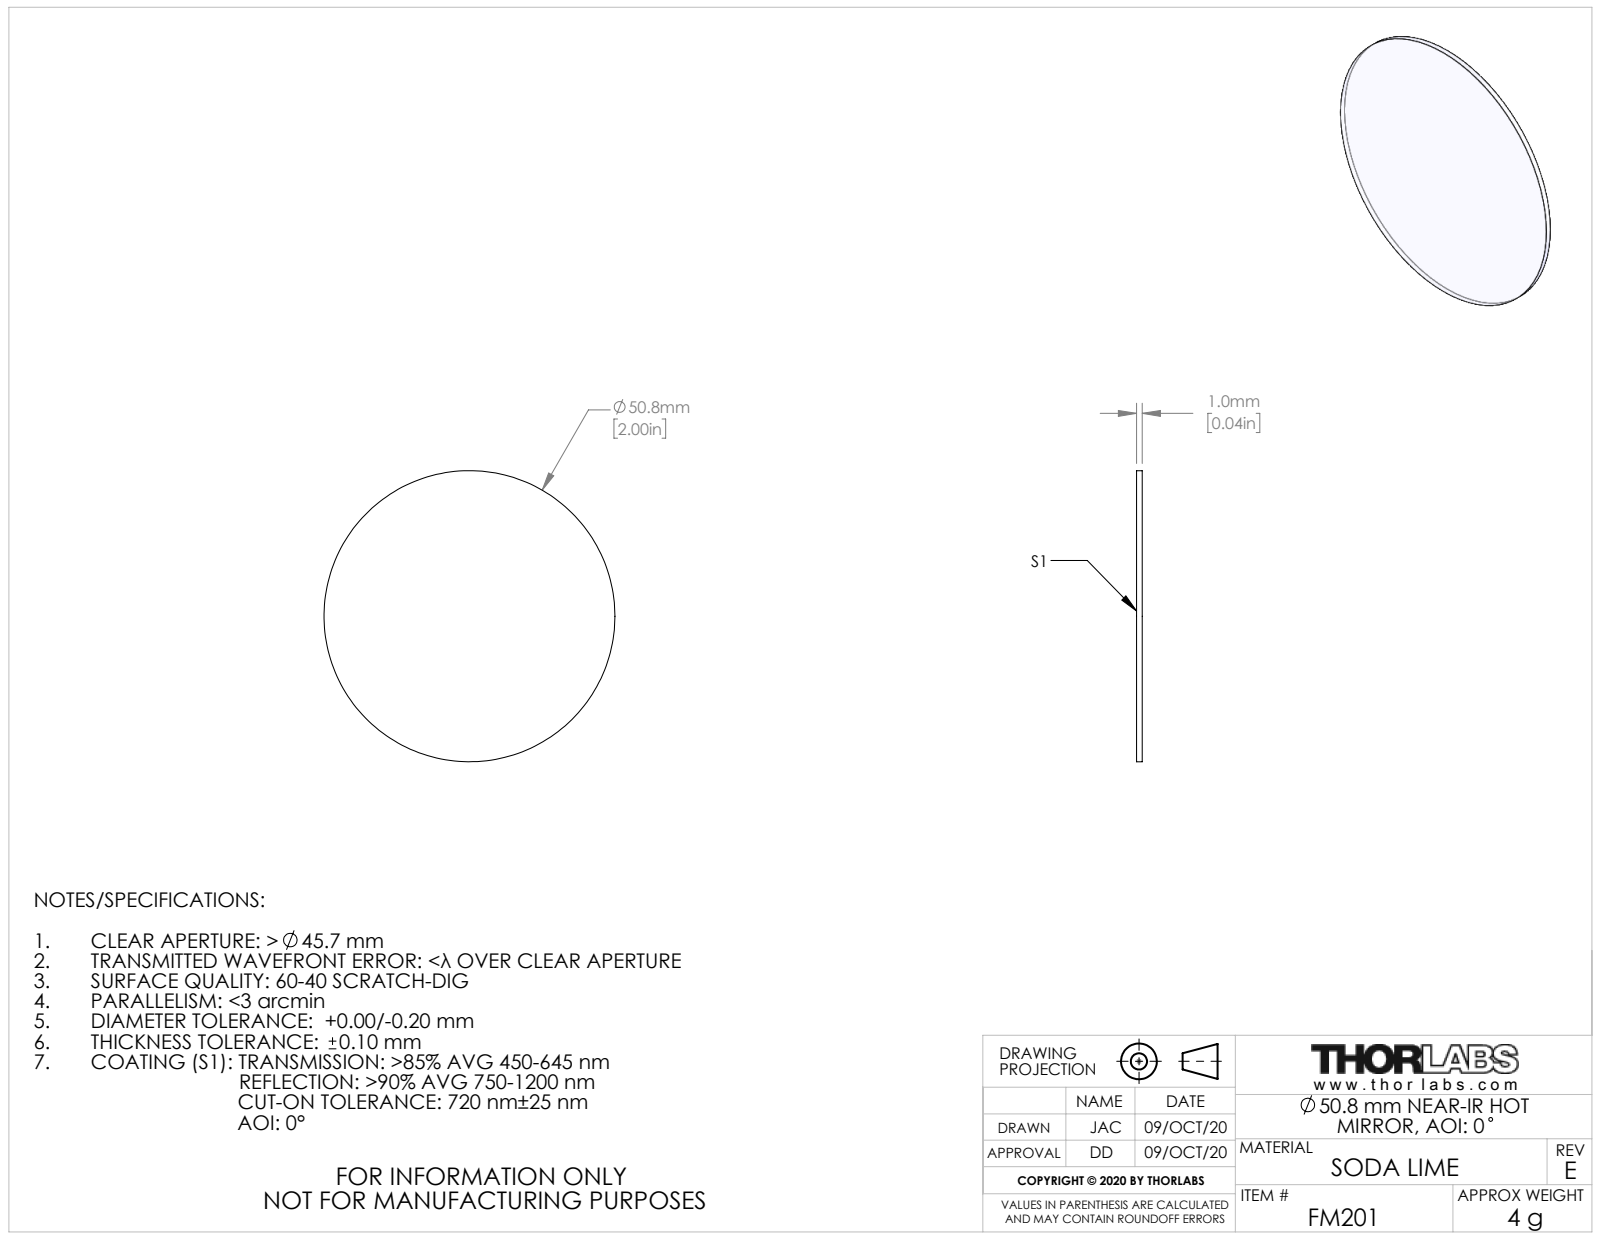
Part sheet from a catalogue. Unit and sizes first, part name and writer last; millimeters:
Units: millimetres
Overall size (bounding box): 50.8 × 50.8 × 1
Round bosses / shafts (diameter × count): ⌀50.8 ×1
Main face-to-face distances: 1
Volume: 2 027 mm³ · Surface area: 4 213 mm²
Bodies: 1 solid, 4 faces (2 planar, 2 cylindrical, 0 other)
Part name (STEP PRODUCT): 10642-E0W
STEP written by: SolidWorks 2018 (CONFIG_CONTROL_DESIGN)
